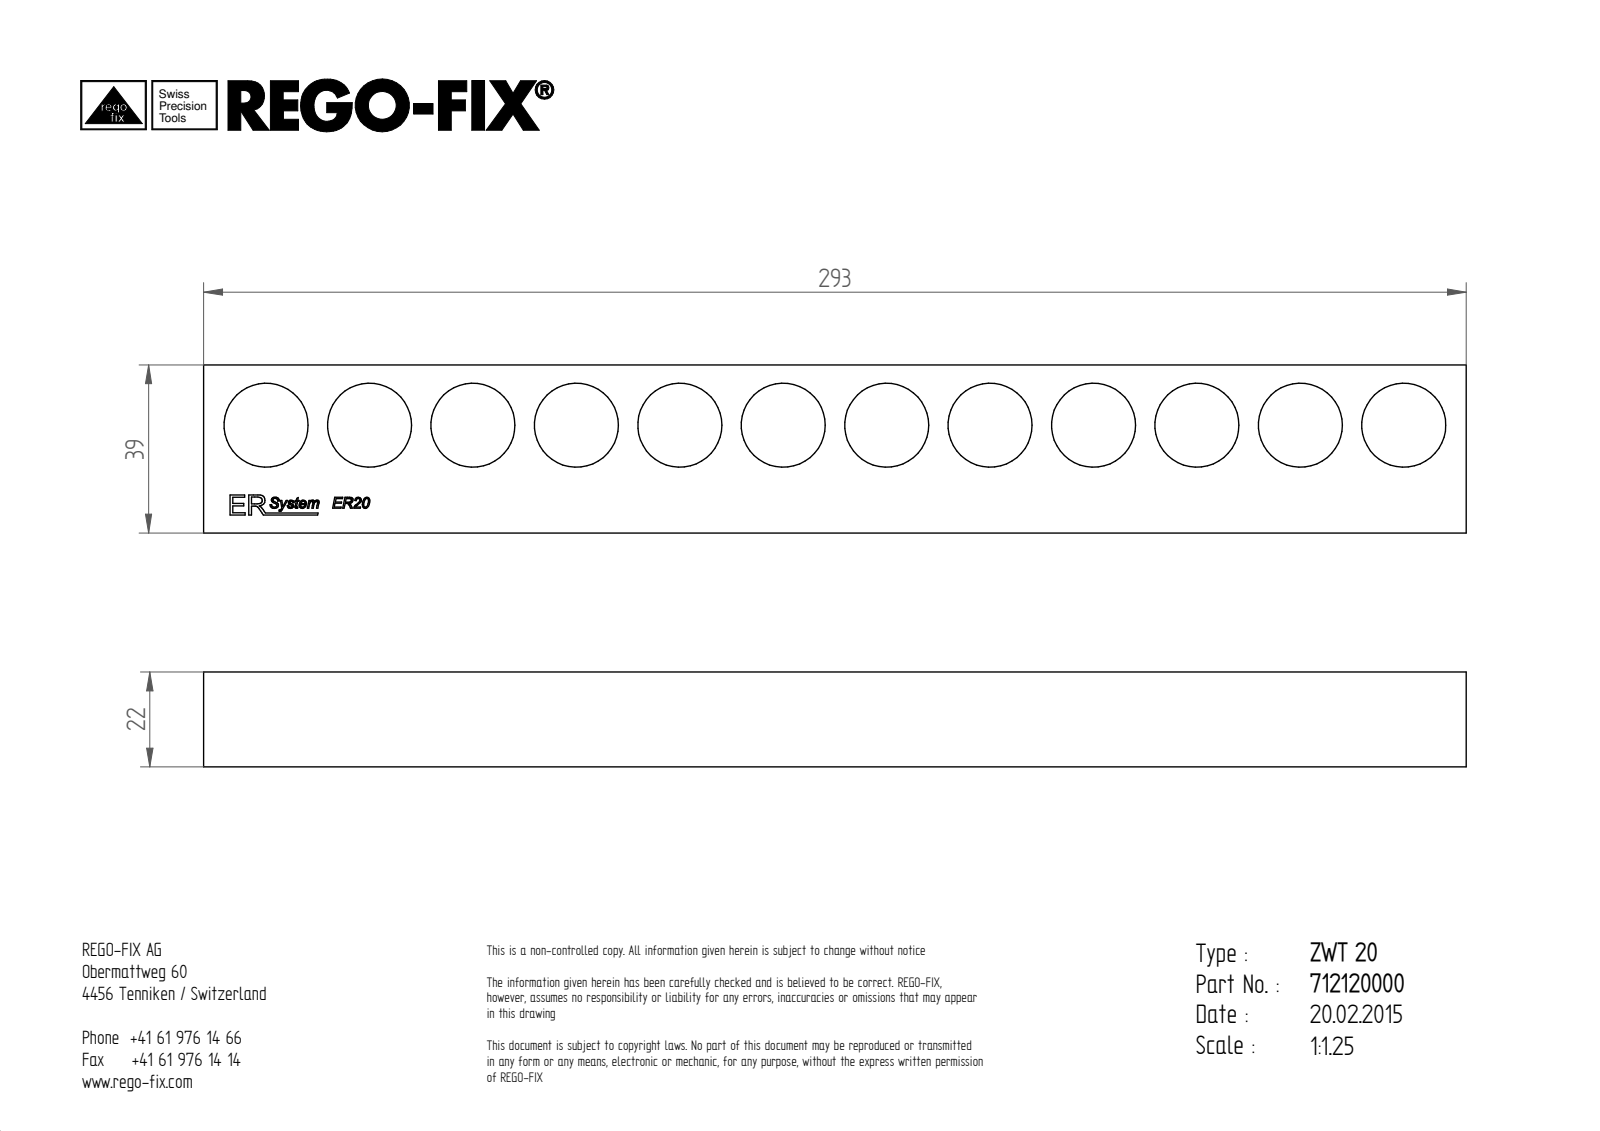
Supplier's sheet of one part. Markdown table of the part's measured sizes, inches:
| quantity | value |
| --- | --- |
| STEP written by | Unknown (AUTOMOTIVE_DESIGN) |
| units | inches |
| bodies | 1 solid, 142 faces (102 planar, 12 cylindrical, 28 other) |
| overall size | 11.535 × 1.535 × 0.866 |
| volume | 11.4 in³ |
| surface area | 78.61 in² |
| round holes (diameter × count) | 0.768 × 12 |
| main face-to-face distances | 0.866, 1.535, 0.157, 0.709, 11.535, 0.862, 0.705, 0.163, 1.373, 0.182 |
| hole center spacings | 0.945, 1.89, 2.835, 3.78, 4.724, 5.669, 6.614, 7.559 |
